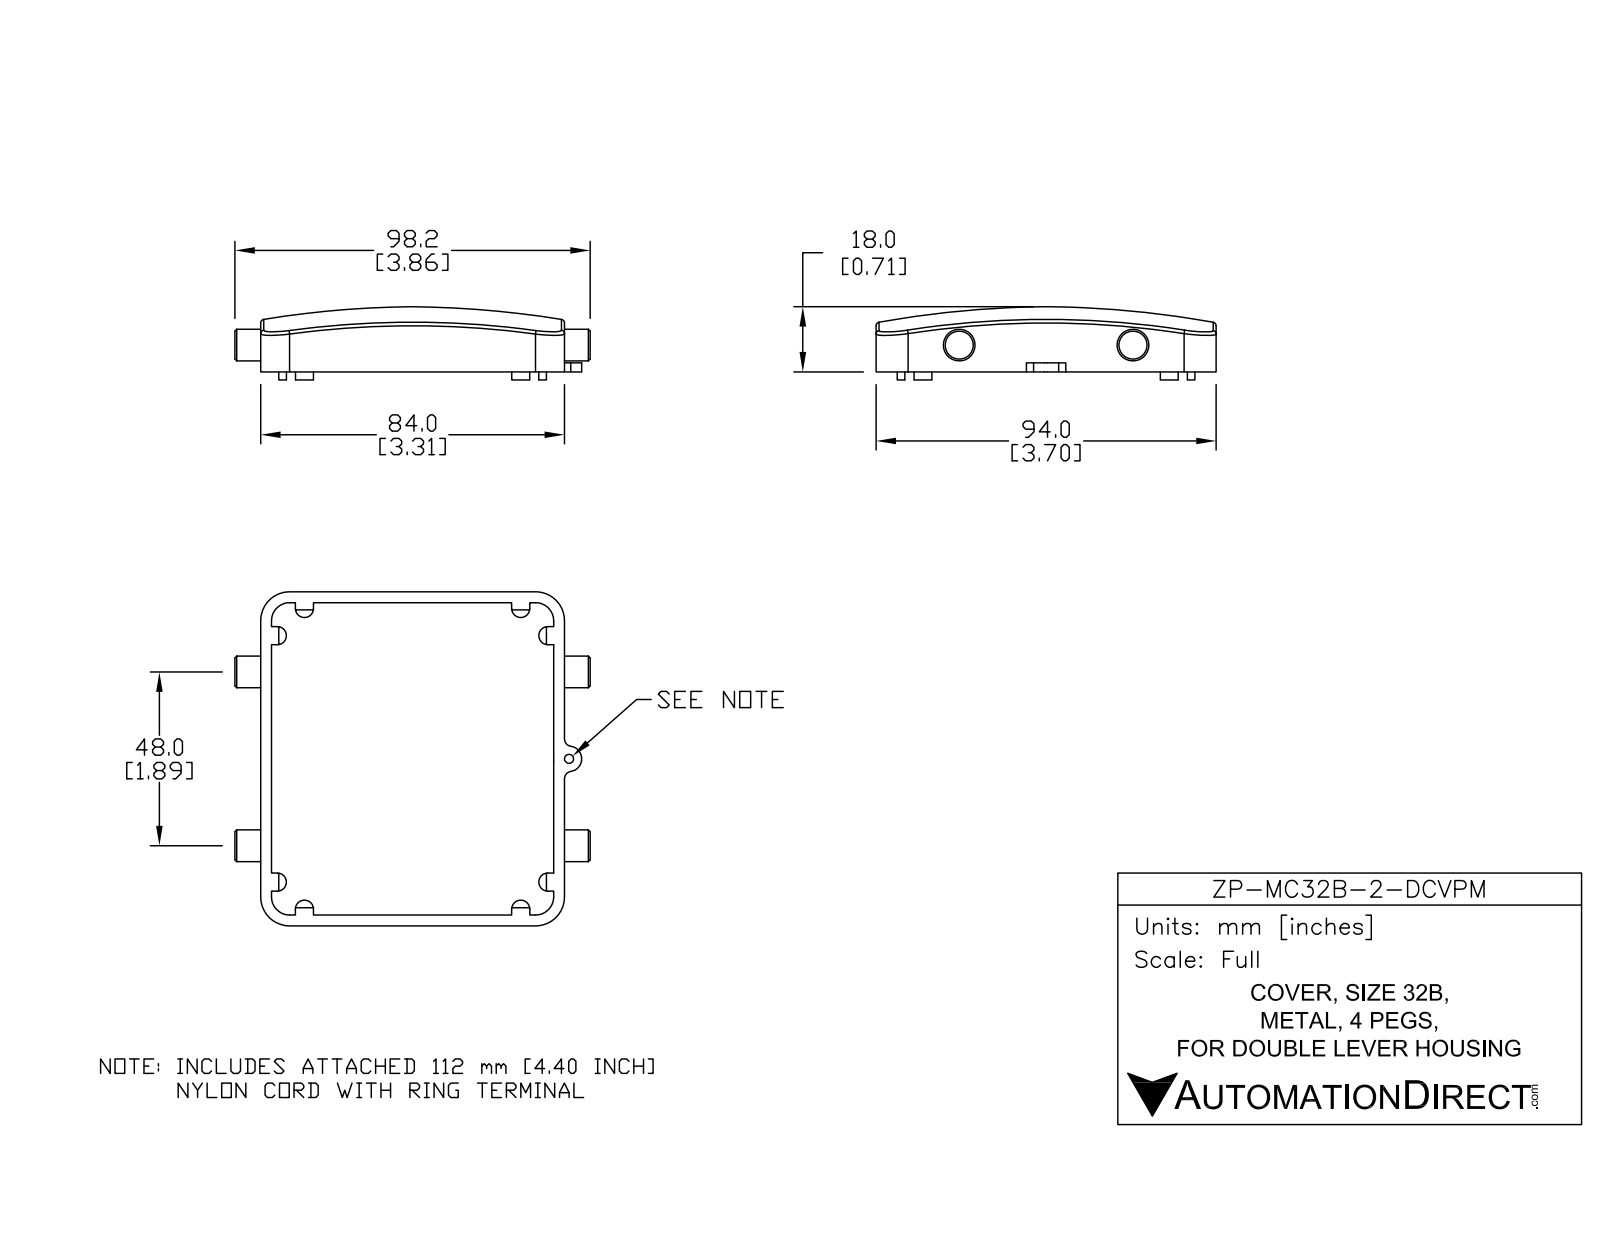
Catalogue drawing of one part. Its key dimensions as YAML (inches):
part_name: "ZP-MC32B-2-DCVPM"
step_written_by: "SolidWorks 2014 (AUTOMOTIVE_DESIGN)"
units: inches
bodies: {solids: 4, faces: 139, planar: 73, cylindrical: 42, other: 24}
overall_size: [7.601, 3.632, 2.626]
volume: 2.196
surface_area: 39.06
round_holes:
  - {diameter: 0.098, count: 1}
  - {diameter: 0.161, count: 1}
round_bosses_or_shafts:
  - {diameter: 0.344, count: 2}
partial_cylinders:
  - {radius: 0.098, count: 8}
  - {radius: 0.018, count: 4}
  - {radius: 0.197, count: 4}
  - {radius: 0.315, count: 4}
  - {radius: 0.024, count: 2}
  - {radius: 0.079, count: 2}
  - {radius: 0.236, count: 2}
  - {radius: 0.138, count: 1}
face_to_face_distances: [0.118, 3.159, 3.514, 3.277, 3.632, 3.041, 3.396, 0.28, 0.398, 3.439]
